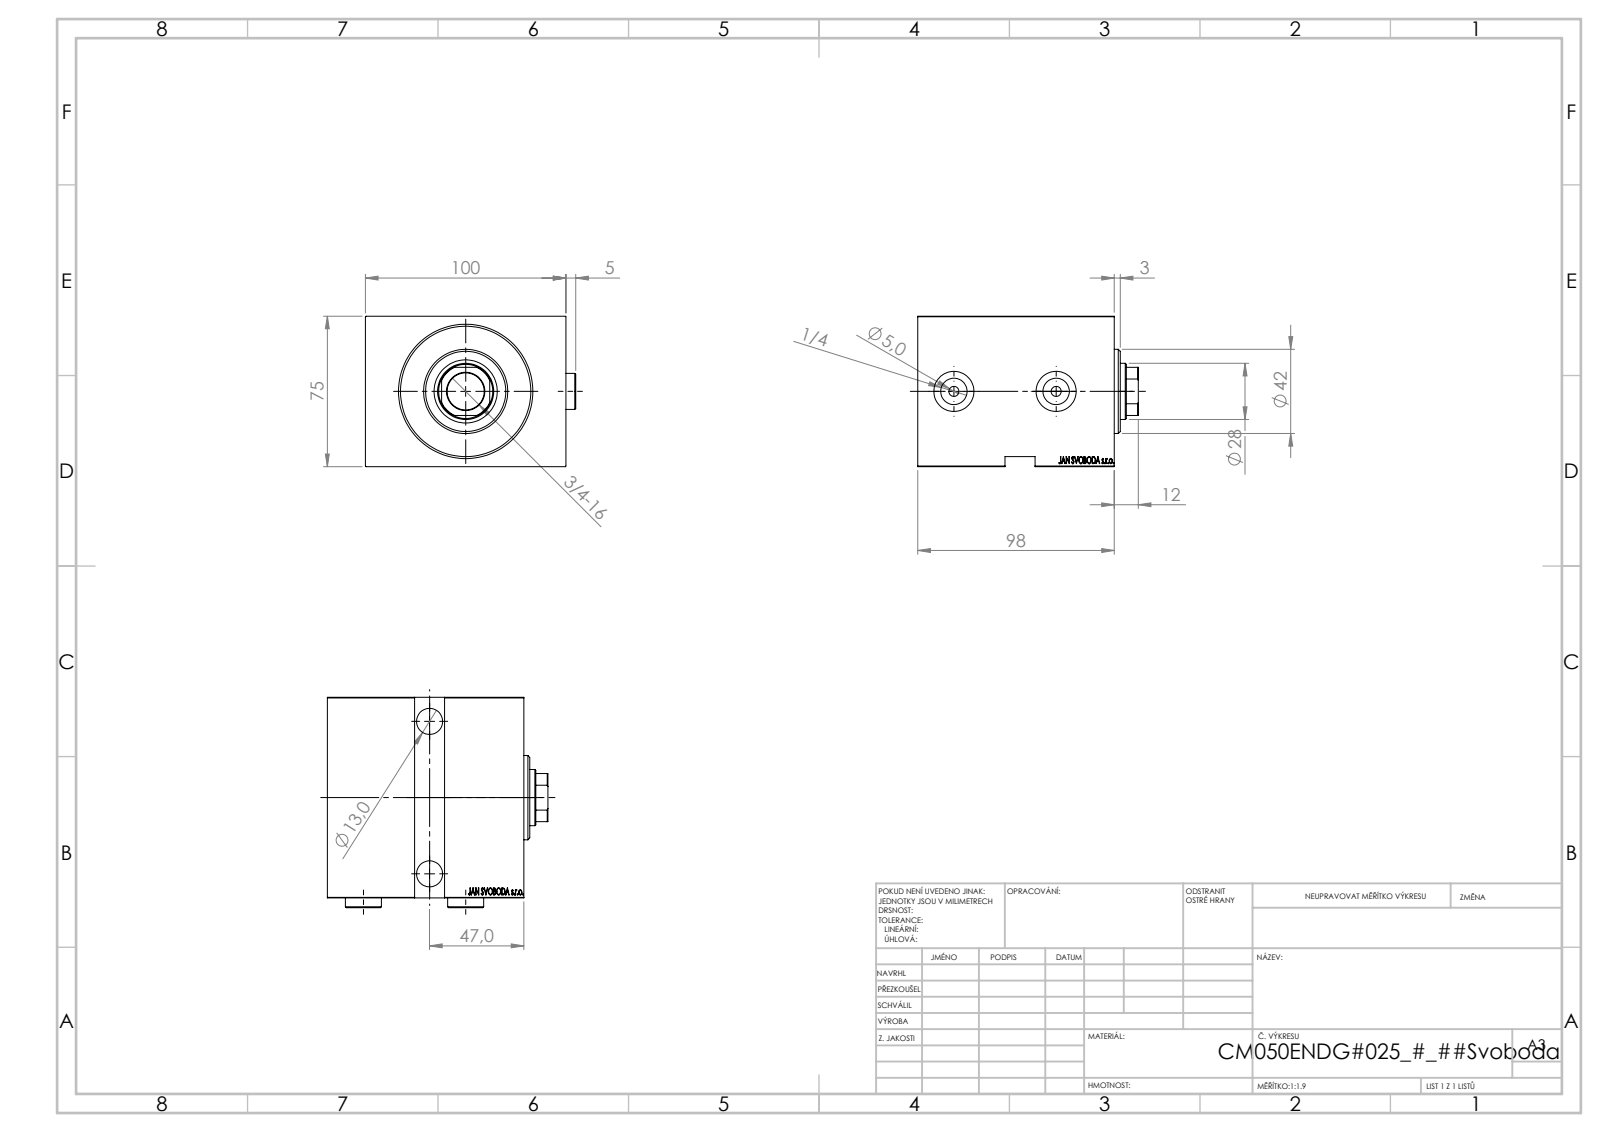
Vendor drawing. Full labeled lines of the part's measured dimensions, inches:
Part name (STEP PRODUCT): V450CM_VC_B; V450CM_E_Body; V450CM_E_VCP; Zatka_OIL_PORT
STEP written by: SolidWorks 2019 (CONFIG_CONTROL_DESIGN)
Units: inches
Bodies: 5 solids, 902 faces (444 planar, 60 cylindrical, 398 other)
Overall size (bounding box): 4.331 × 4.13 × 2.953
Volume: 41.16 in³ · Surface area: 157.7 in²
Round holes (diameter × count): ⌀0.197 ×2, ⌀0.512 ×2, ⌀0.518 ×2, ⌀0.748 ×2, ⌀0.787 ×2, ⌀0.728 ×1, ⌀1.102 ×1, ⌀1.24 ×1, ⌀1.969 ×1, ⌀2.559 ×1
Round bosses / shafts (diameter × count): ⌀0.709 ×2, ⌀2.047 ×1, ⌀1.654 ×1
Partial cylindrical surfaces — rounded edges, fillets, slot ends (radius × count): R0.531 ×1
Main face-to-face distances: 2.953, 3.937, 3.858, 0.197, 0.551, 3.307, 3.11, 3.661, 0.512, 2.598
Hole centre spacings: 2.008, 2.992
